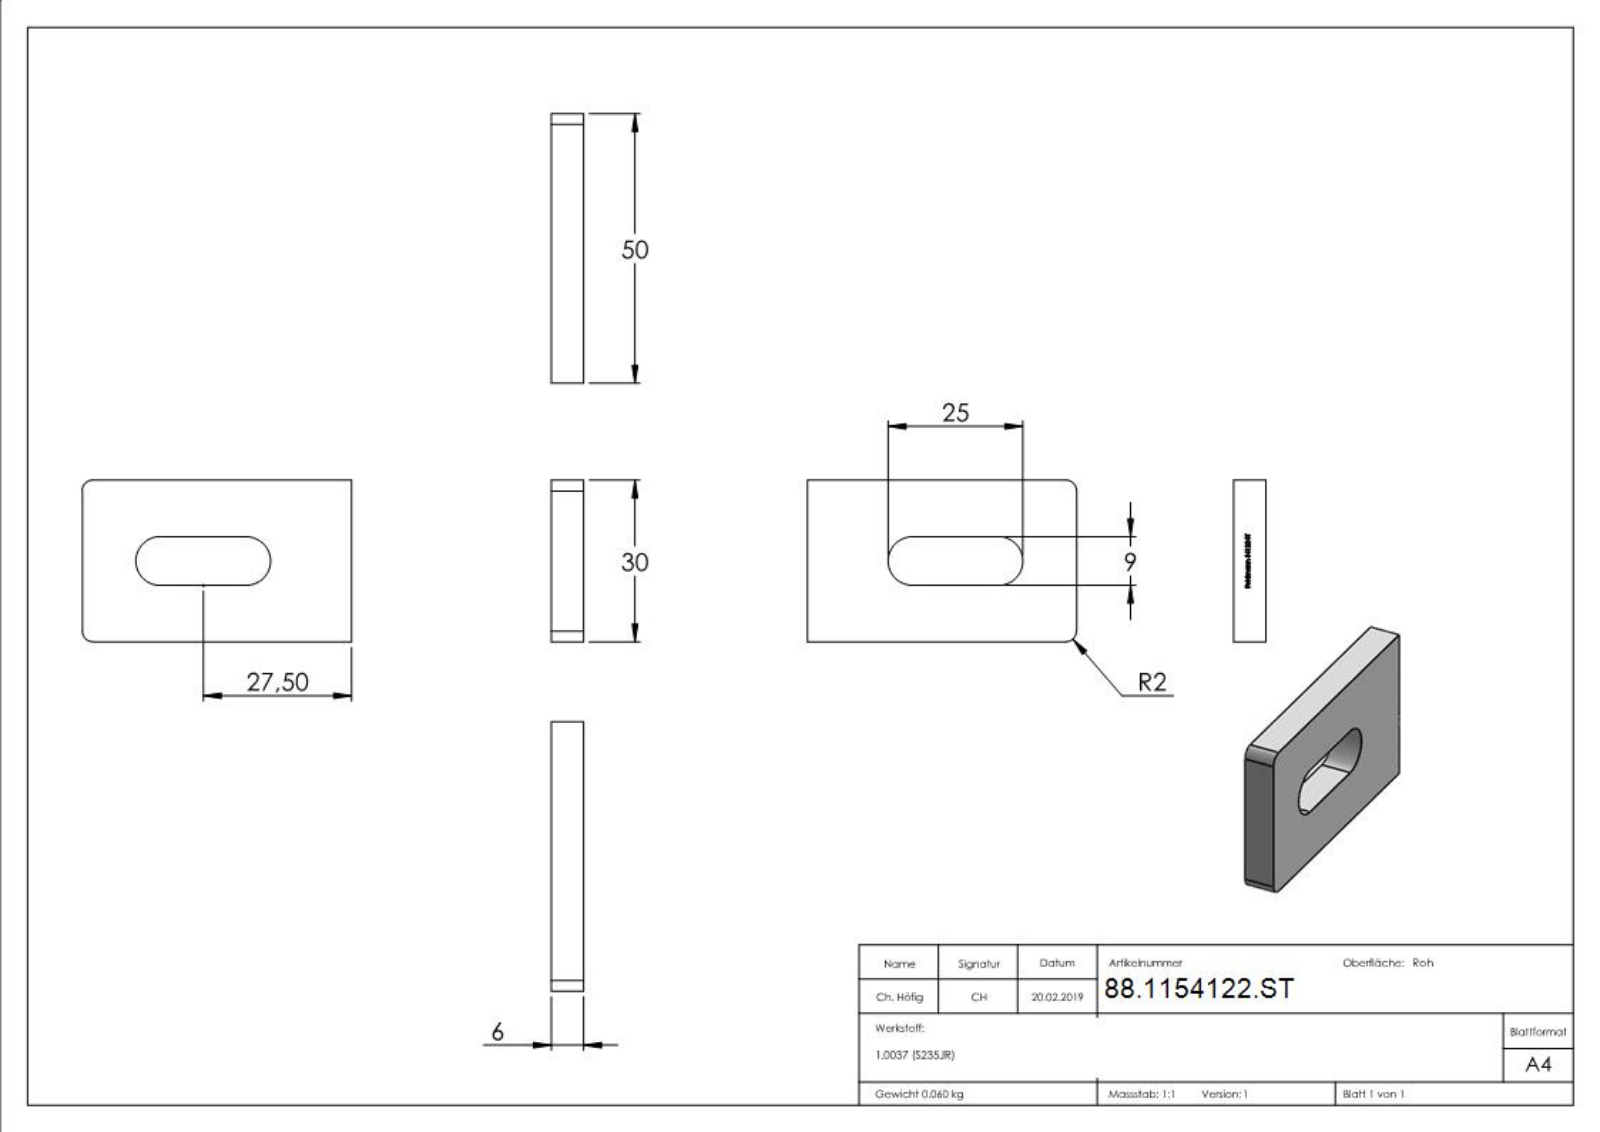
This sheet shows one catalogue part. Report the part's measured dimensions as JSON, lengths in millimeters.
{"part_name": "54122-ST", "step_written_by": "SolidWorks 2015 (CONFIG_CONTROL_DESIGN)", "units": "millimeters", "bodies": {"solids": 1, "faces": 221, "planar": 133, "cylindrical": 5, "other": 83}, "overall_size": [50, 30, 6], "volume_mm3": 7744, "surface_area_mm2": 3898, "partial_cylinders_radius": [[2, 2], [4.5, 2]], "face_to_face_distances": [6, 30, 10.5, 19.5, 50, 9, 49.9, 3, 0.44, 0.71]}
